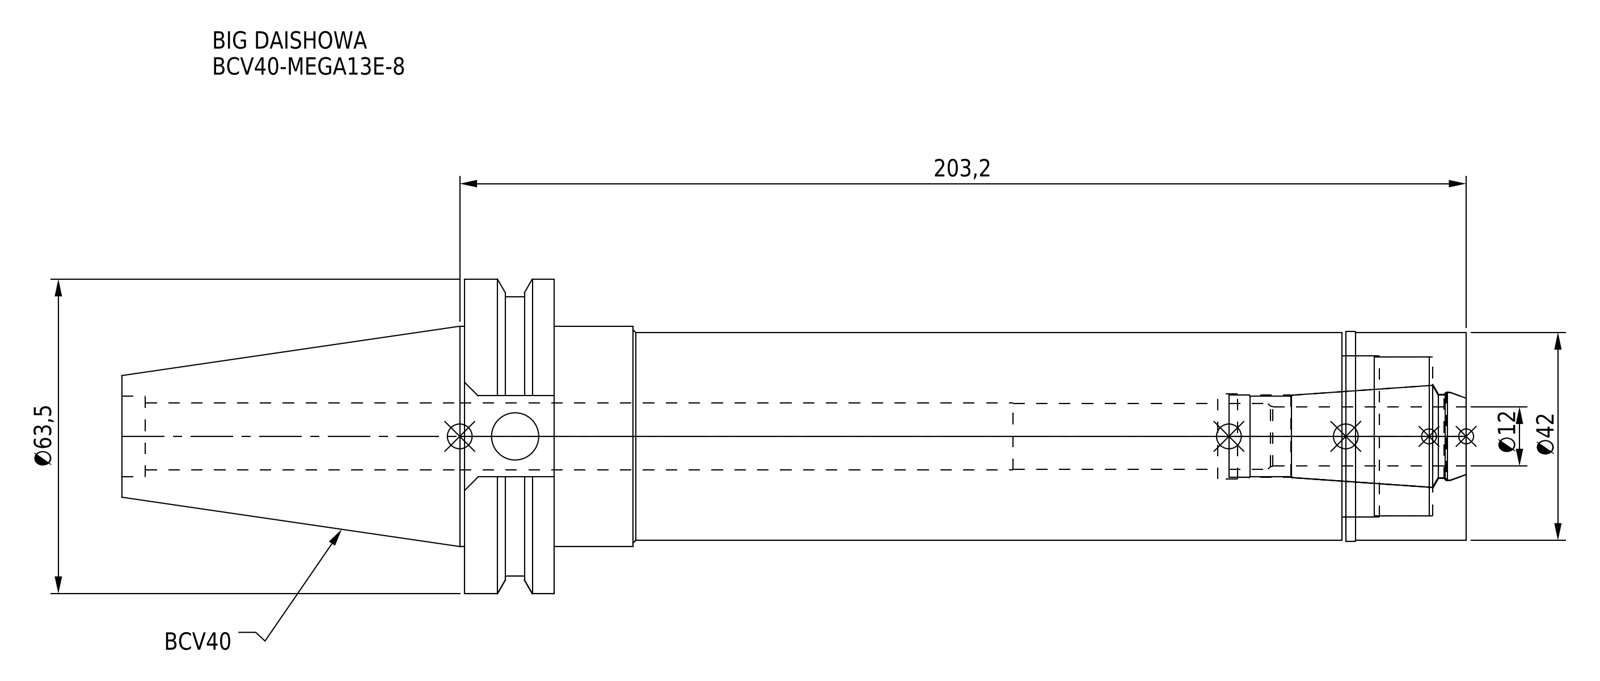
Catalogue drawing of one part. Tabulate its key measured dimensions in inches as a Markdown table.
| quantity | value |
| --- | --- |
| part name | BCV40-MEGA13E-8-120-FreeParts; BCV40-MEGA13E-8_1.stp; MEN13_1.stp; DXF_TEMP_ASSY_ASM_4_ASM.stp (+3 more) |
| STEP written by | SolidWorks 2019 (CONFIG_CONTROL_DESIGN) |
| units | inches |
| bodies | 2 solids, 90 faces (30 planar, 42 cylindrical, 18 other) |
| overall size | 10.687 × 2.5 × 2.415 |
| volume | 20.08 in³ |
| surface area | 91.5 in² |
| round holes (diameter × count) | 0.375 × 1, 0.524 × 1, 0.535 × 1, 0.643 × 1, 0.654 × 1, 0.669 × 1, 0.677 × 1, 0.705 × 1, 1.26 × 1, 1.28 × 1 |
| round bosses / shafts (diameter × count) | 2.5 × 1, 2.219 × 1, 1.75 × 1, 1.665 × 1, 1.654 × 1 |
| main face-to-face distances | 0.711, 7.25, 7.961, 0.988, 0.957, 6.293, 7.004, 0.031, 6.262, 6.972 |
